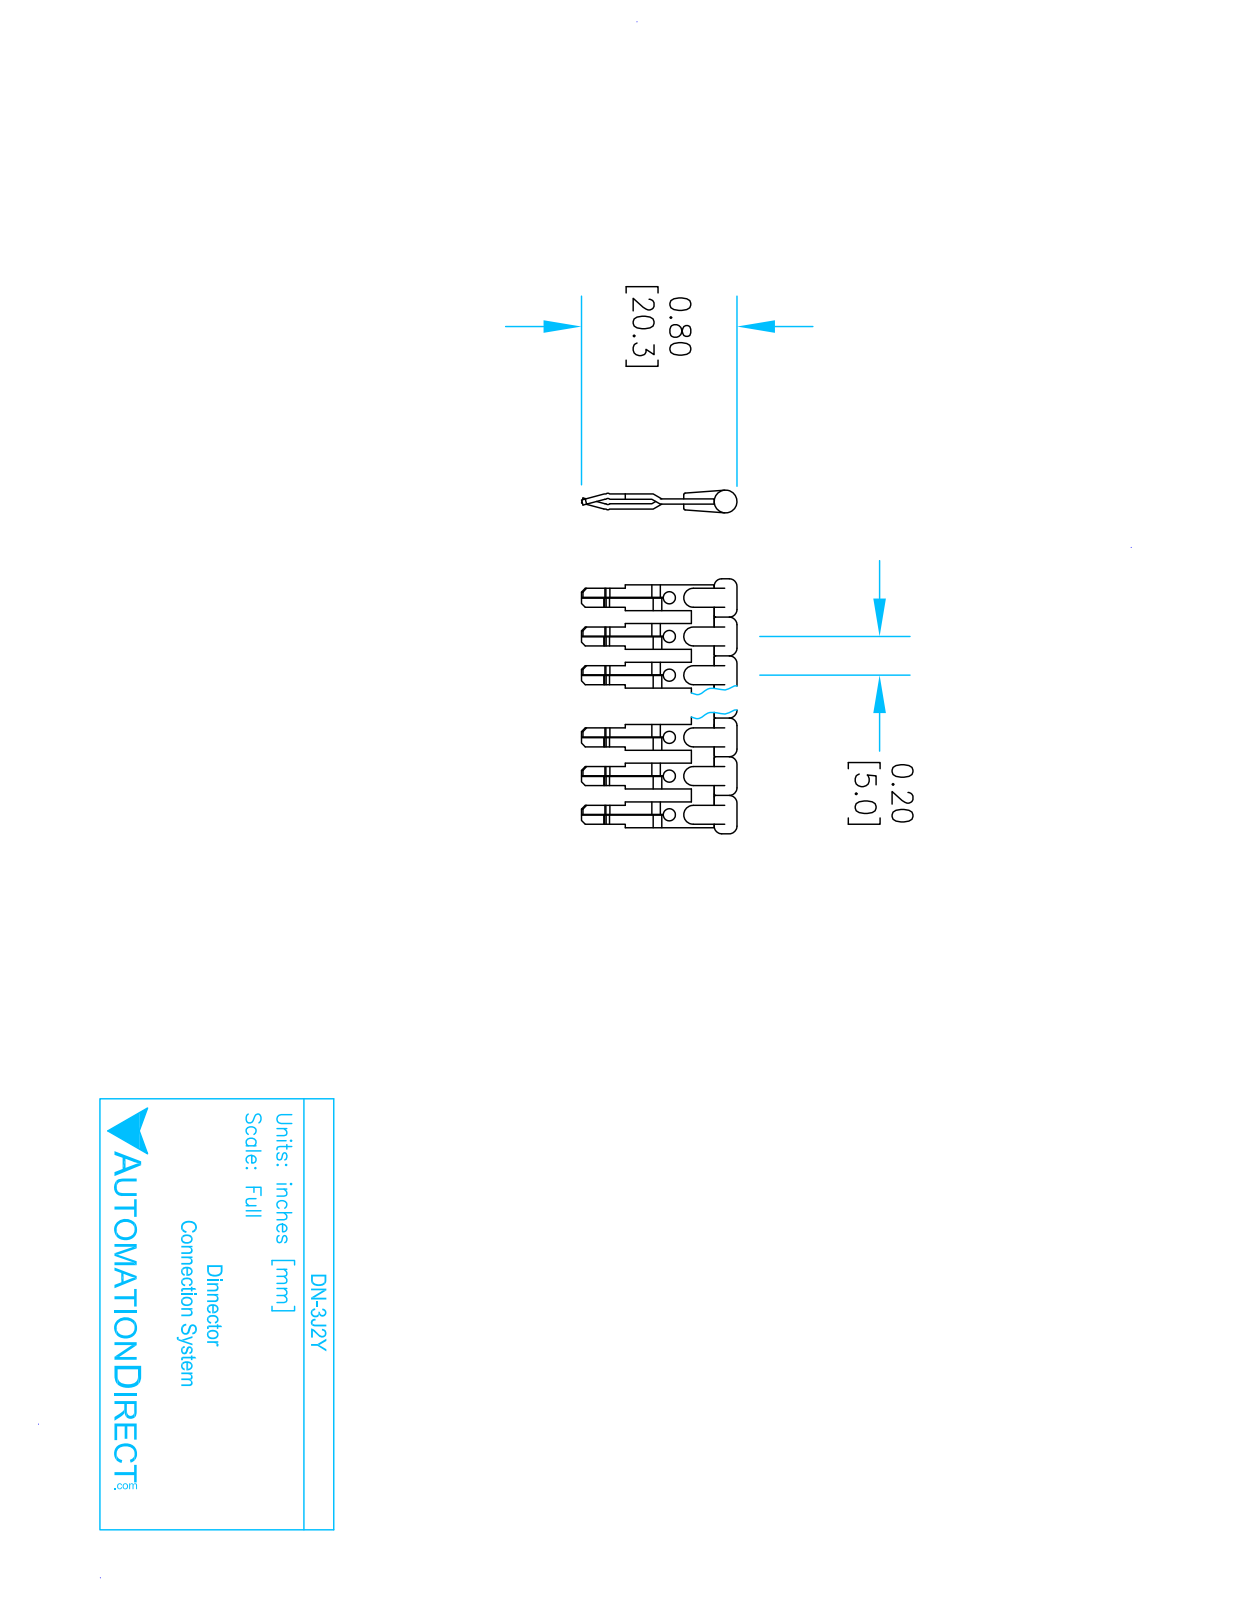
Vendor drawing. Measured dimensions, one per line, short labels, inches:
name: J2,5_J4 INTERMEDIO; 43525_03_DN-3J2Y; J2,5_M; J2,5_M_intermedio
written by: SolidWorks 2013 (AUTOMOTIVE_DESIGN)
unit: in
bodies: 6 solids, 191 faces (113 planar, 48 cylindrical, 30 other)
size: 0.801 × 0.597 × 0.118
volume: 0.018 in³; area: 1.18 in²
holes: 6× ⌀0.051
bosses: 1× ⌀0.118
rounds: 12× R0.02, 4× R0.028, 3× R0.049
face distances: 0.028, 0.022, 0.071, 0.049, 0.043, 0.201, 0.067, 0.2, 0.401, 0.016
hole spacings: 0.162, 0.2, 0.201, 0.258, 0.258, 0.401, 0.433
